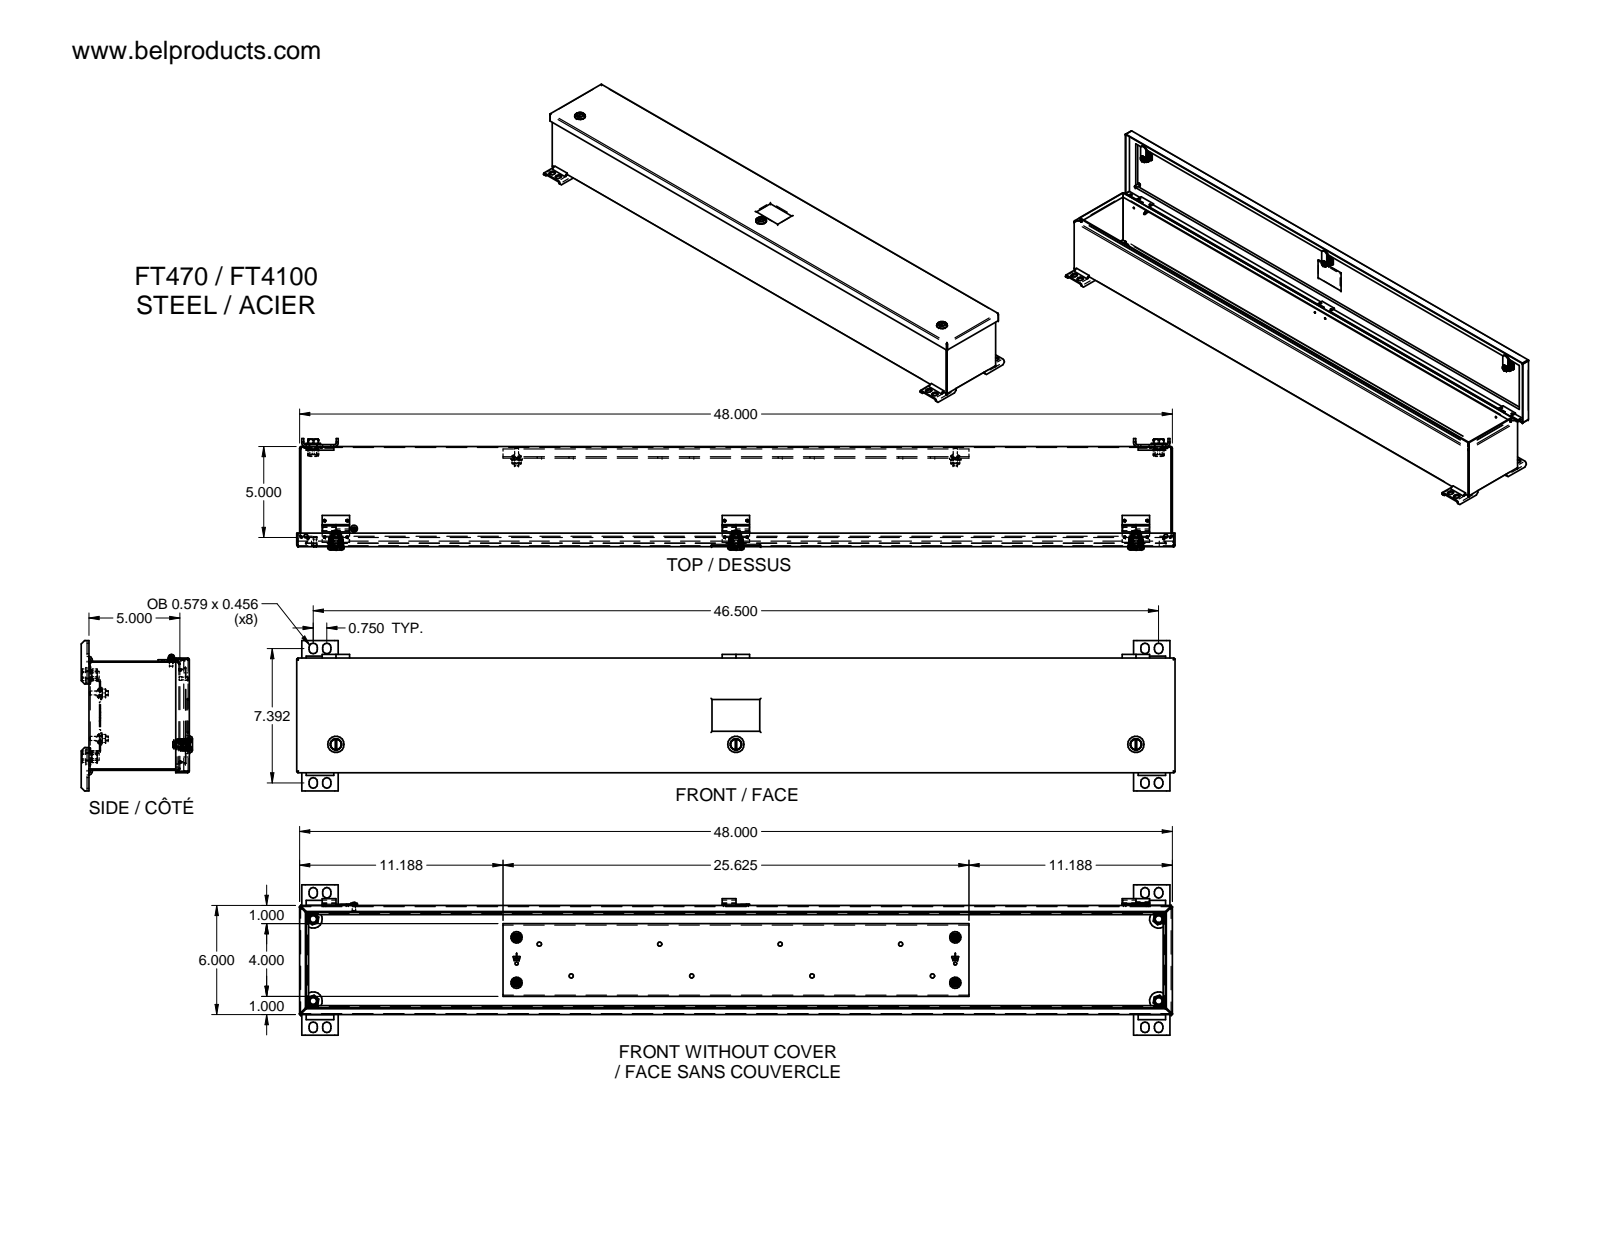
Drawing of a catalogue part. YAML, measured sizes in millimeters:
part_name: "LOCK AVEC TOURNEVIS TYPE 4-12 SANS CAME-oa8; HOSING-oa0; INSERT POUR TOURNEVIS-oa1; NOIX DE FIXATION-oa2 (+8 more)"
step_written_by: "Unknown (AUTOMOTIVE_DESIGN)"
units: millimeters
bodies: {solids: 76, faces: 2767, planar: 1582, cylindrical: 524, other: 661}
overall_size: [1226.82, 209.96, 155.57]
volume: 1818000
surface_area: 2041000
round_holes:
  - {diameter: 3.16, count: 12}
  - {diameter: 3.3, count: 12}
  - {diameter: 5.99, count: 8}
  - {diameter: 9.53, count: 8}
  - {diameter: 11.58, count: 8}
  - {diameter: 3.17, count: 5}
  - {diameter: 6.35, count: 4}
  - {diameter: 7.14, count: 4}
  - {diameter: 9.02, count: 4}
  - {diameter: 10.31, count: 4}
  - {diameter: 10.54, count: 4}
  - {diameter: 12.7, count: 4}
round_bosses_or_shafts:
  - {diameter: 3.17, count: 12}
  - {diameter: 3.02, count: 5}
  - {diameter: 20.62, count: 4}
  - {diameter: 15.88, count: 4}
  - {diameter: 5.56, count: 4}
  - {diameter: 0.79, count: 4}
  - {diameter: 22.86, count: 3}
  - {diameter: 22.61, count: 3}
partial_cylinders:
  - {radius: 9.53, count: 32}
  - {radius: 0.25, count: 24}
  - {radius: 0.81, count: 18}
  - {radius: 2.34, count: 16}
  - {radius: 5.79, count: 16}
  - {radius: 1.52, count: 8}
  - {radius: 1.59, count: 8}
  - {radius: 9.42, count: 6}
face_to_face_distances: [1.52, 150.88, 1.53, 138.53, 140.06, 137.01, 138.54, 152.4, 149.36, 1.91]
hole_center_spacings: [558.8, 23.03, 559.27, 31.75, 39.22, 558.79, 559.26, 17.46]
